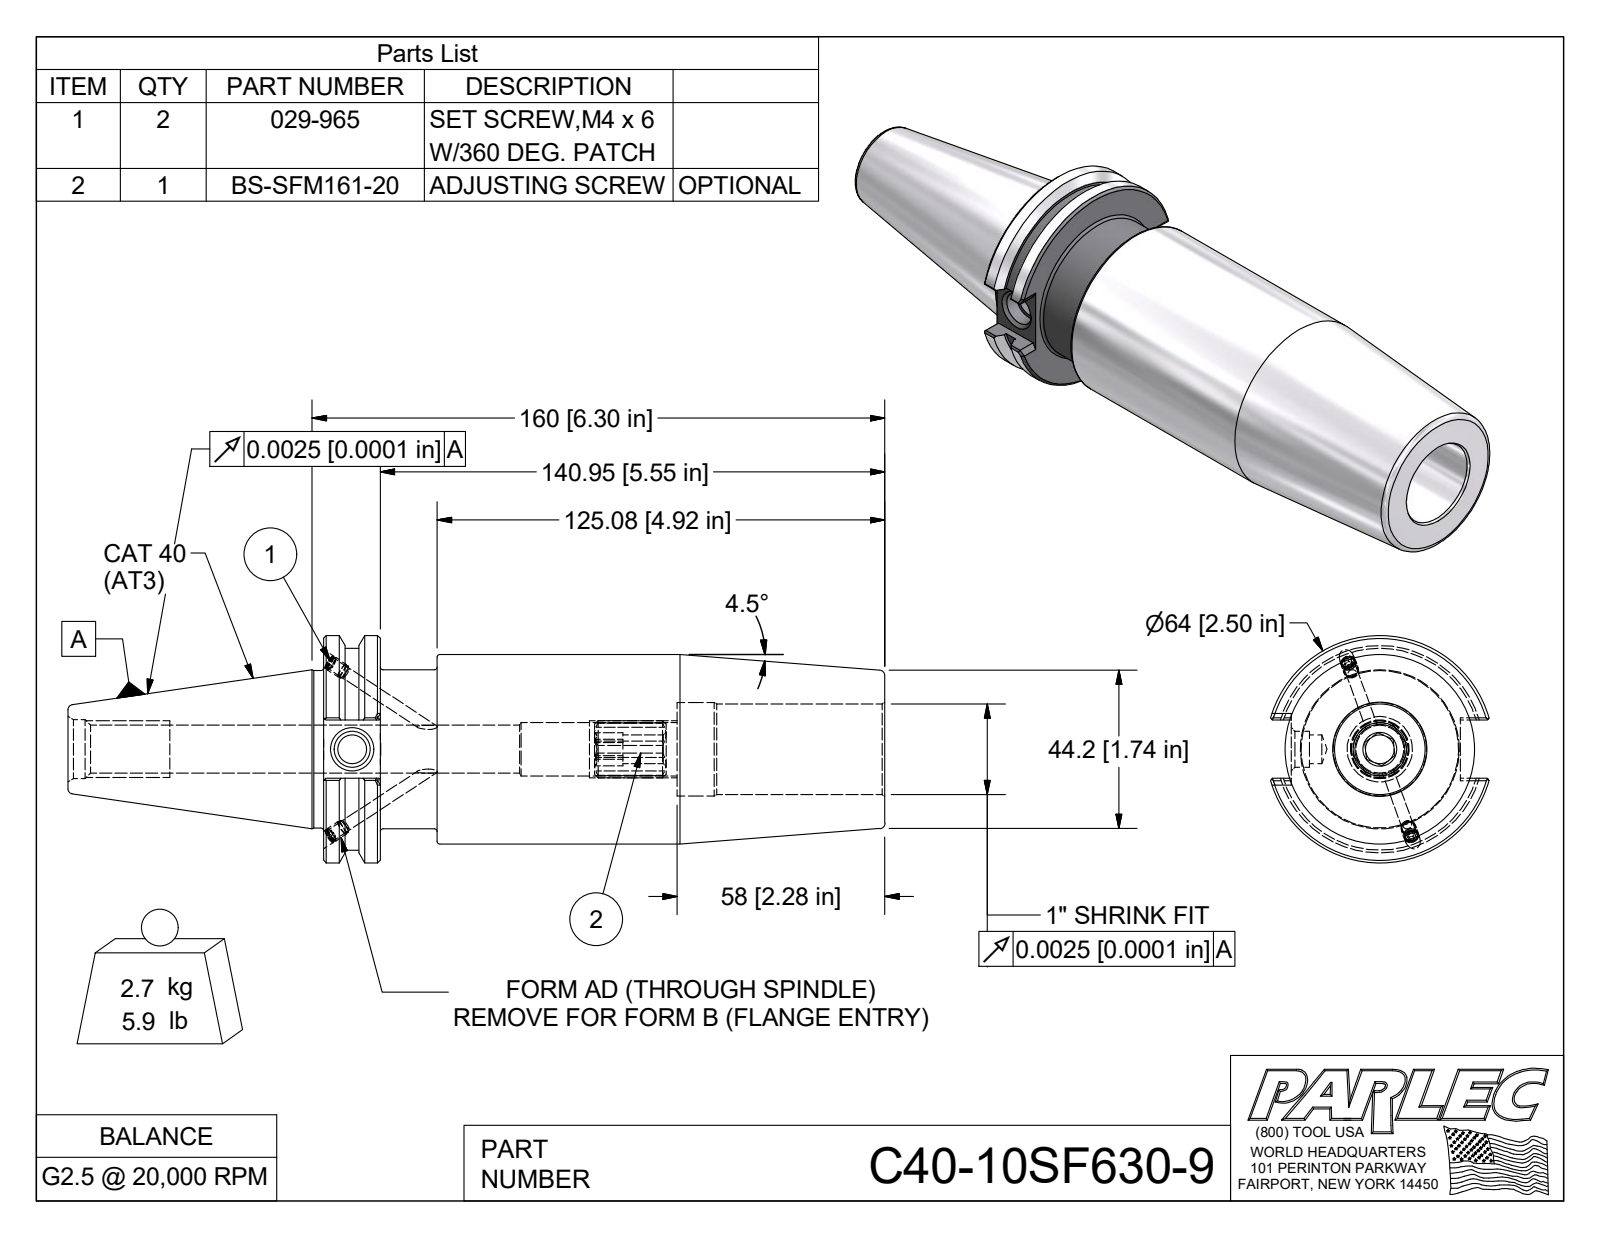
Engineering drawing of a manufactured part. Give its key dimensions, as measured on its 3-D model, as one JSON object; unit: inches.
{"part_name": "C40-10SF630-9; C40BC-10SF630-9-1; 029-965; BS-SFM161-20", "step_written_by": "Autodesk Inventor 2009 (AUTOMOTIVE_DESIGN)", "units": "inches", "bodies": {"solids": 4, "faces": 133, "planar": 66, "cylindrical": 23, "other": 44}, "overall_size": [8.987, 2.5, 2.403], "volume_in3": 20.75, "surface_area_in2": 83.46, "round_holes": [[0.13, 2], [0.161, 2], [0.999, 1], [1.029, 1]], "round_bosses_or_shafts": [[0.165, 2], [0.157, 2], [2.5, 1], [2.219, 1], [2.087, 1], [1.75, 1], [1.73, 1]], "partial_cylinders_radius": [[0.315, 1]], "face_to_face_distances": [0.625, 6.174, 5.549, 1.25, 4.924, 3.891, 3.266, 2.641, 2.283, 0.64]}
